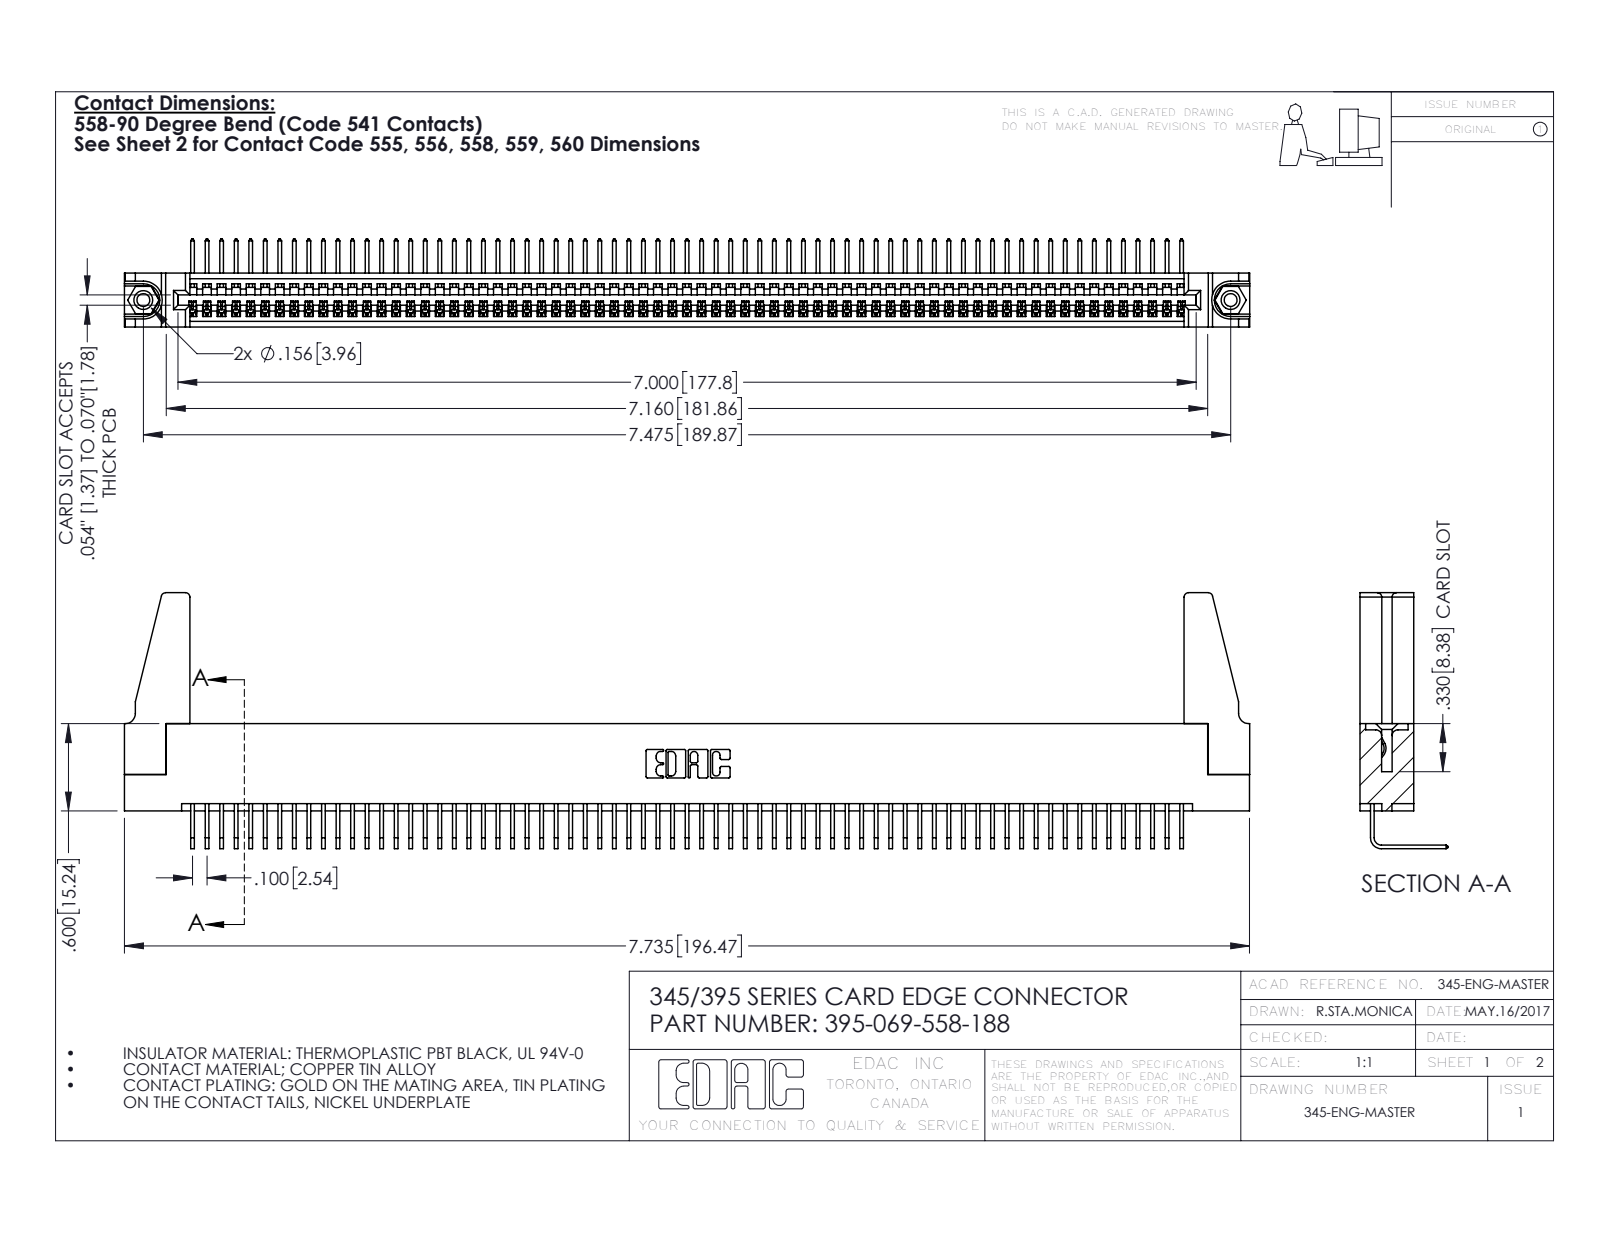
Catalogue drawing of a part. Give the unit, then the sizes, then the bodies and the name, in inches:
Units: inches
Overall size (bounding box): 7.736 × 1.759 × 0.605
Round holes (diameter × count): ⌀0.089 ×2, ⌀0.125 ×2, ⌀0.156 ×2, ⌀0.064 ×1
Round bosses / shafts (diameter × count): ⌀0.155 ×2
Partial cylindrical surfaces — rounded edges, fillets, slot ends (radius × count): R0.006 ×138, R0.01 ×22, R0.03 ×8, R0.007 ×6, R0.031 ×6, R0.026 ×3, R0.031 ×2, R0.04 ×2
Main face-to-face distances: 0.072, 0.298, 0.37, 0.2, 0.098, 0.272, 0.025, 0.225, 0.149, 0.072
Hole centre spacings: 0.27, 7.239, 7.475
Volume: 1.365 in³ · Surface area: 46.88 in²
Bodies: 74 solids, 4390 faces (3050 planar, 1324 cylindrical, 16 other)
Part name (STEP PRODUCT): 345 Part_Flush Mounting Lugs - 0.156 Dia-TH; 345-220-078_345-220-088; 395-069-558-188; 345-250-001_345-250-001-102 (+1 more)
STEP written by: SolidWorks 2016 (CONFIG_CONTROL_DESIGN)
